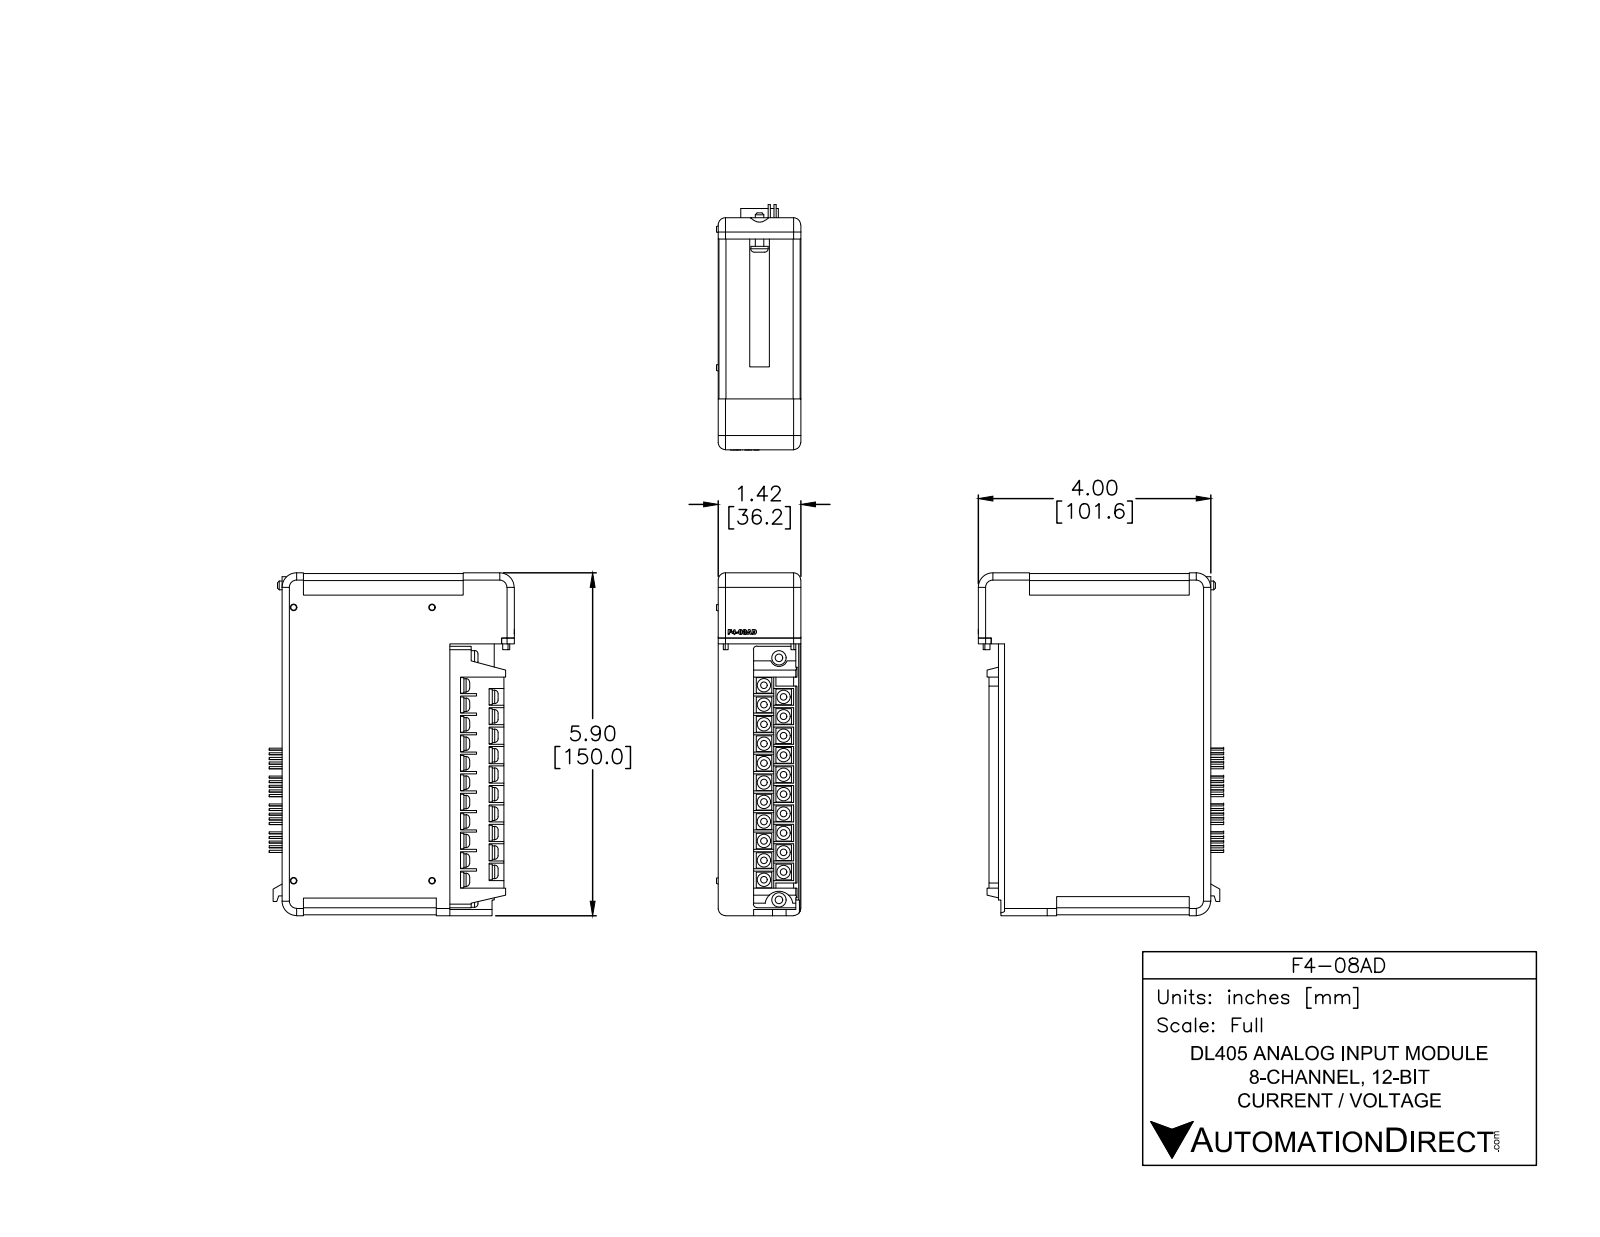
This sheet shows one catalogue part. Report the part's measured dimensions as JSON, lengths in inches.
{"part_name": "F4-08AD", "step_written_by": "SolidWorks 2014 (AUTOMOTIVE_DESIGN)", "units": "inches", "bodies": {"solids": 6, "faces": 884, "planar": 544, "cylindrical": 246, "other": 94}, "overall_size": [5.905, 4.223, 1.455], "volume_in3": 27.6, "surface_area_in2": 90.48, "round_bosses_or_shafts": [[0.23, 21], [0.035, 20], [0.035, 20], [0.25, 2], [0.3, 1], [0.15, 1]], "partial_cylinders_radius": [[0.015, 82], [0.125, 8], [0.12, 4], [0.25, 3], [0.03, 2], [0.06, 2], [0.149, 1], [0.151, 1]], "face_to_face_distances": [1.425, 0.015, 2.89, 5.875, 1.41, 0.47, 0.955, 5.89, 1.21, 0.345]}
